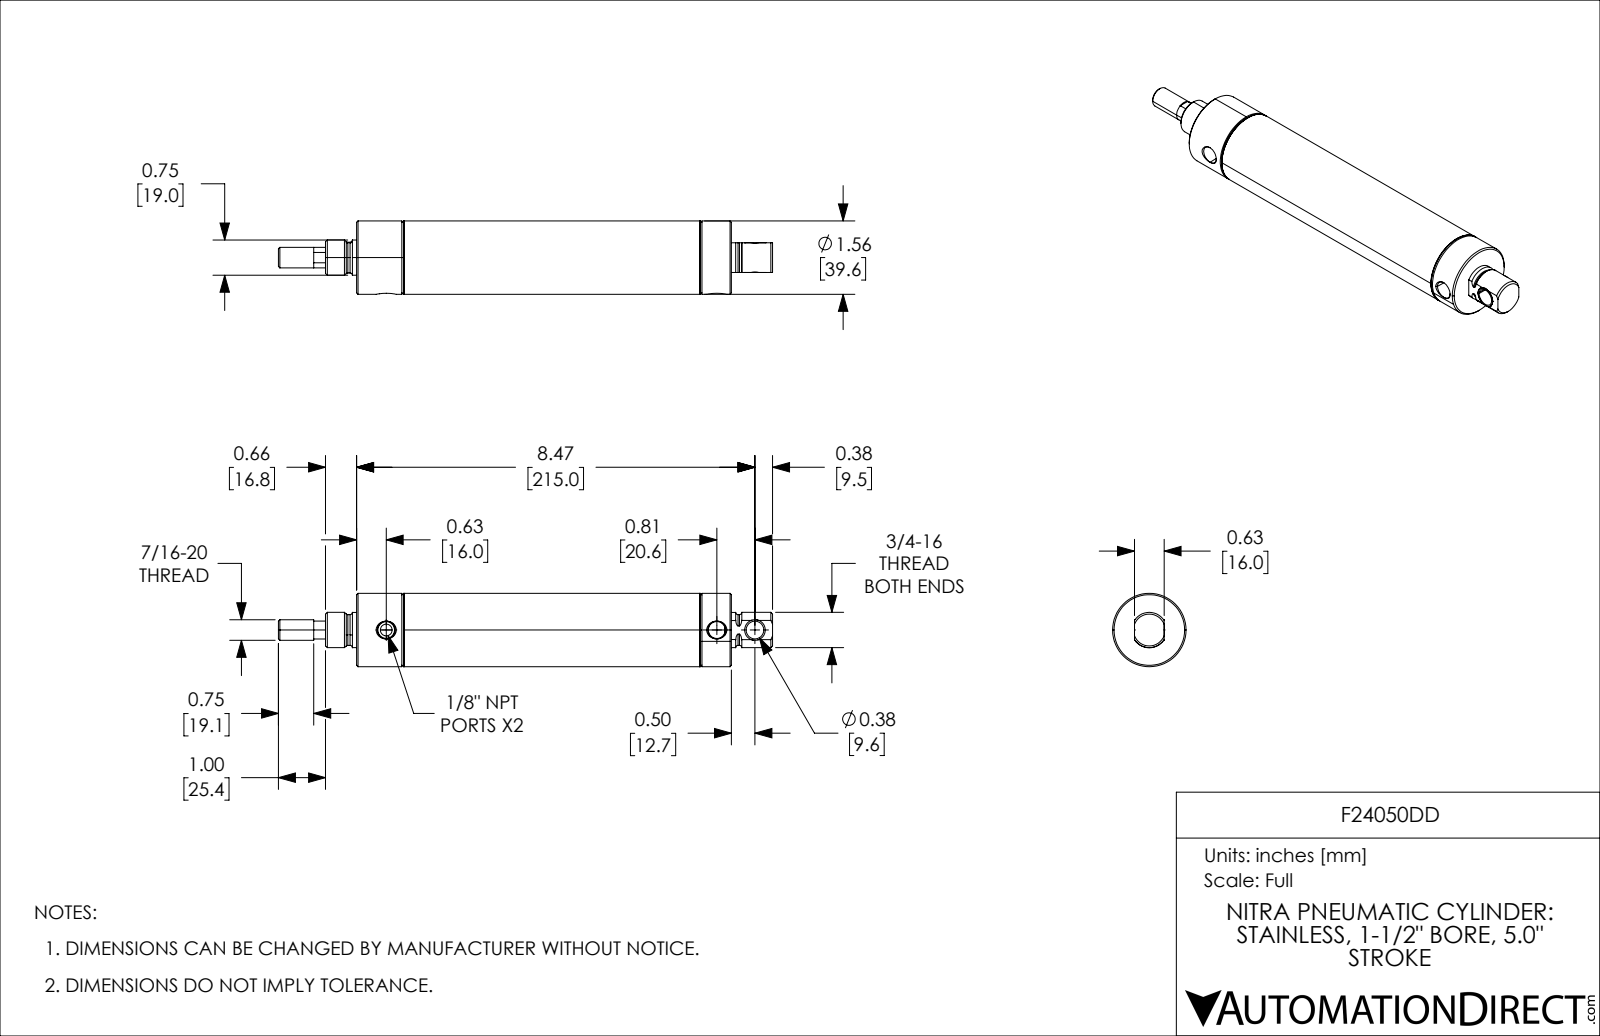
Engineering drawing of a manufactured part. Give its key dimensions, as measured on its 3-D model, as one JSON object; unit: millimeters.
{"part_name": "F24050DD; F24050DD_9; F24050DD_7; F24050DD_11 (+2 more)", "step_written_by": "SolidWorks 2021 (CONFIG_CONTROL_DESIGN)", "units": "millimeters", "bodies": {"solids": 5, "faces": 157, "planar": 35, "cylindrical": 58, "other": 64}, "overall_size": [266.7, 39.62, 39.62], "volume_mm3": 117545, "surface_area_mm2": 71178, "round_holes": [[6.35, 1], [9.14, 1], [9.55, 1], [11.15, 1], [11.73, 1], [13.51, 1], [26.97, 1], [36.36, 1]], "round_bosses_or_shafts": [[39.62, 1], [38.39, 1], [19.05, 1], [18.99, 1], [16.61, 1], [16.6, 1], [11.13, 1], [11.11, 1]], "face_to_face_distances": [22.22, 44.45, 127, 149.22, 171.45, 22.23, 30.86, 157.86, 180.08, 202.31], "hole_center_spacings": [20.57, 178.44, 199.01]}
